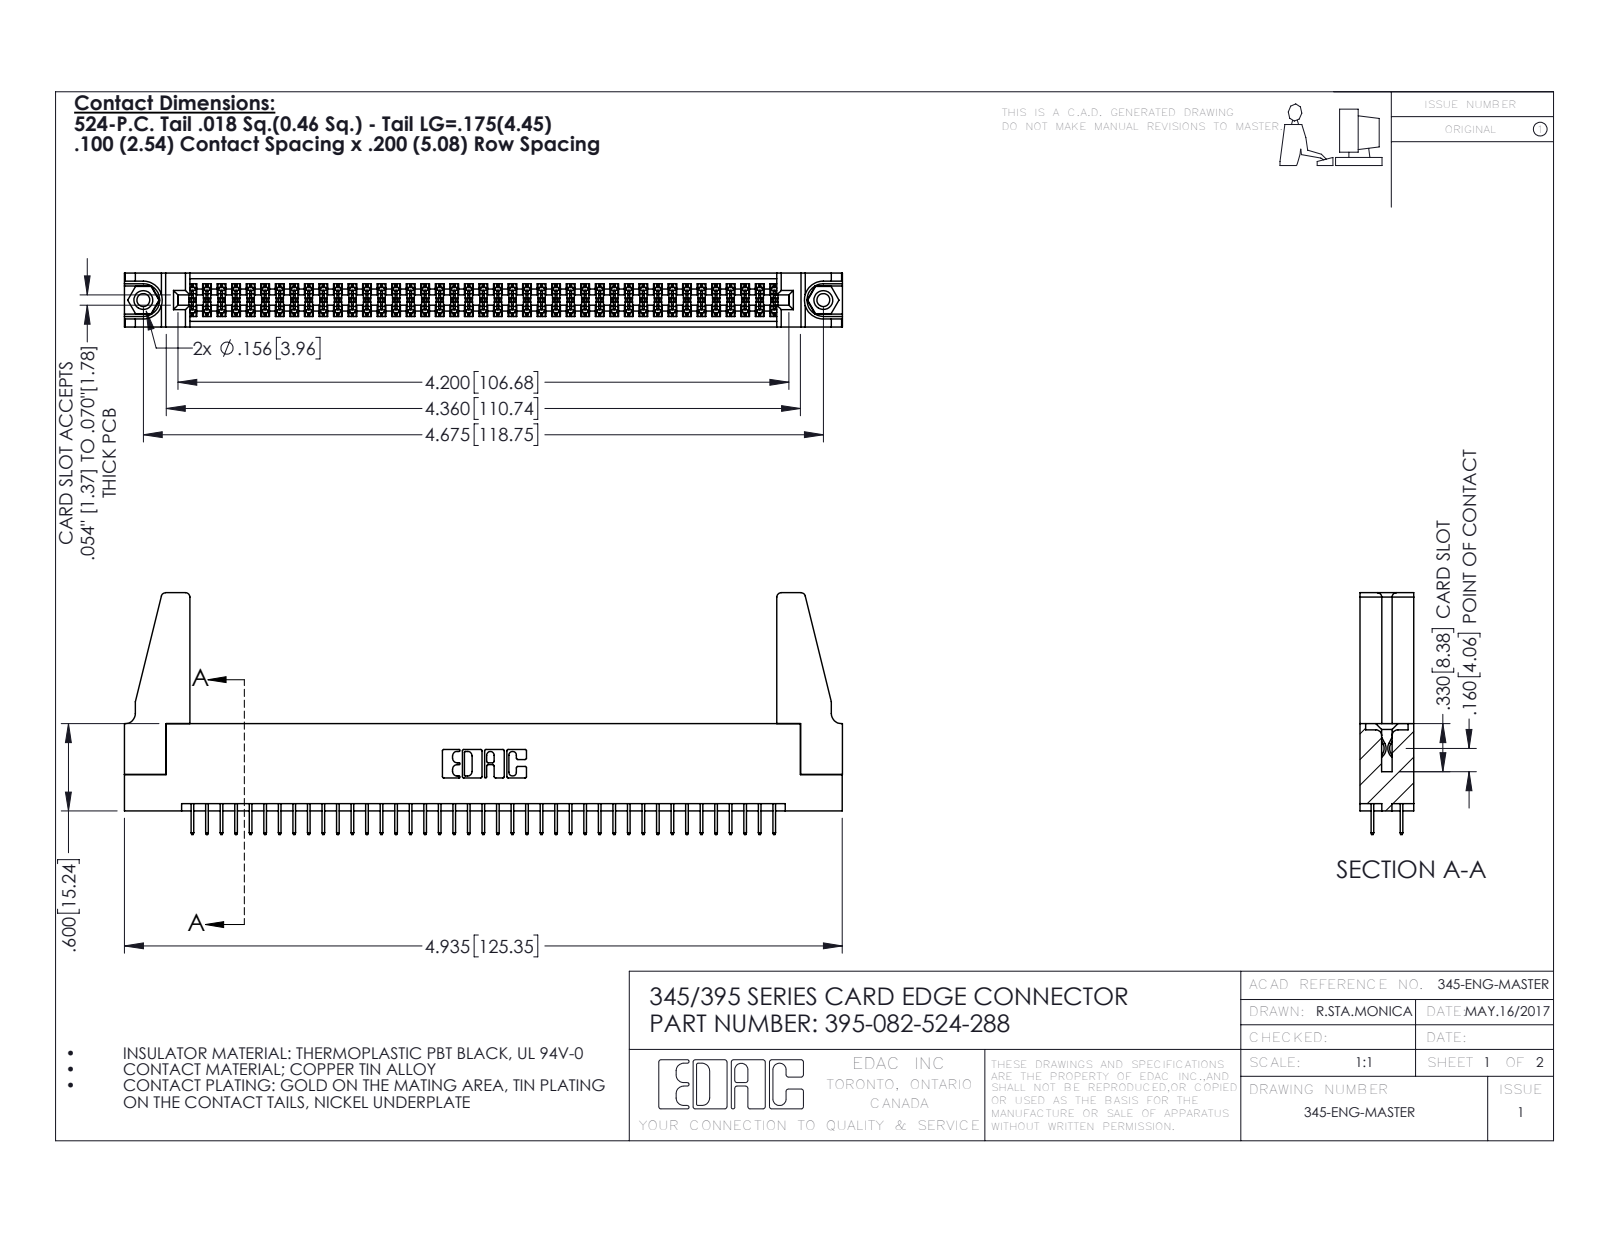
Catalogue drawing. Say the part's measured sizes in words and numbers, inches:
The part is named "395-082-524-288; 345-292-001_345-293-124; 345 Part_Flush Mounting Lugs - 0.156 Dia-TH; 345-250-001_345-250-001-102 (+1 more)". Its 3-D file was written by "SolidWorks 2016 (CONFIG_CONTROL_DESIGN)". It is 87 solids with 4678 faces: 3350 planar, 1312 cylindrical and 16 other. Overall it measures 4.936 by 1.662 by 0.37 inches. Its volume is 0.934 cubic inches and its surface area 31.9 square inches. Round holes: 2 of diameter 0.089, 2 of diameter 0.125, 2 of diameter 0.156, 1 of diameter 0.064. Round bosses or shafts: 2 of diameter 0.155. Partial cylindrical surfaces (rounded edges, fillets, slot ends): 123 of radius 0.006, 22 of radius 0.01, 8 of radius 0.03, 6 of radius 0.007, 6 of radius 0.031, 3 of radius 0.026, 2 of radius 0.014, 2 of radius 0.019. The main face-to-face distances are 0.072, 0.298, 0.37, 0.2, 0.098, 0.272, 0.025, 0.225, 0.072, 0.175. The hole center spacings are 0.27, 4.439, 4.675.
